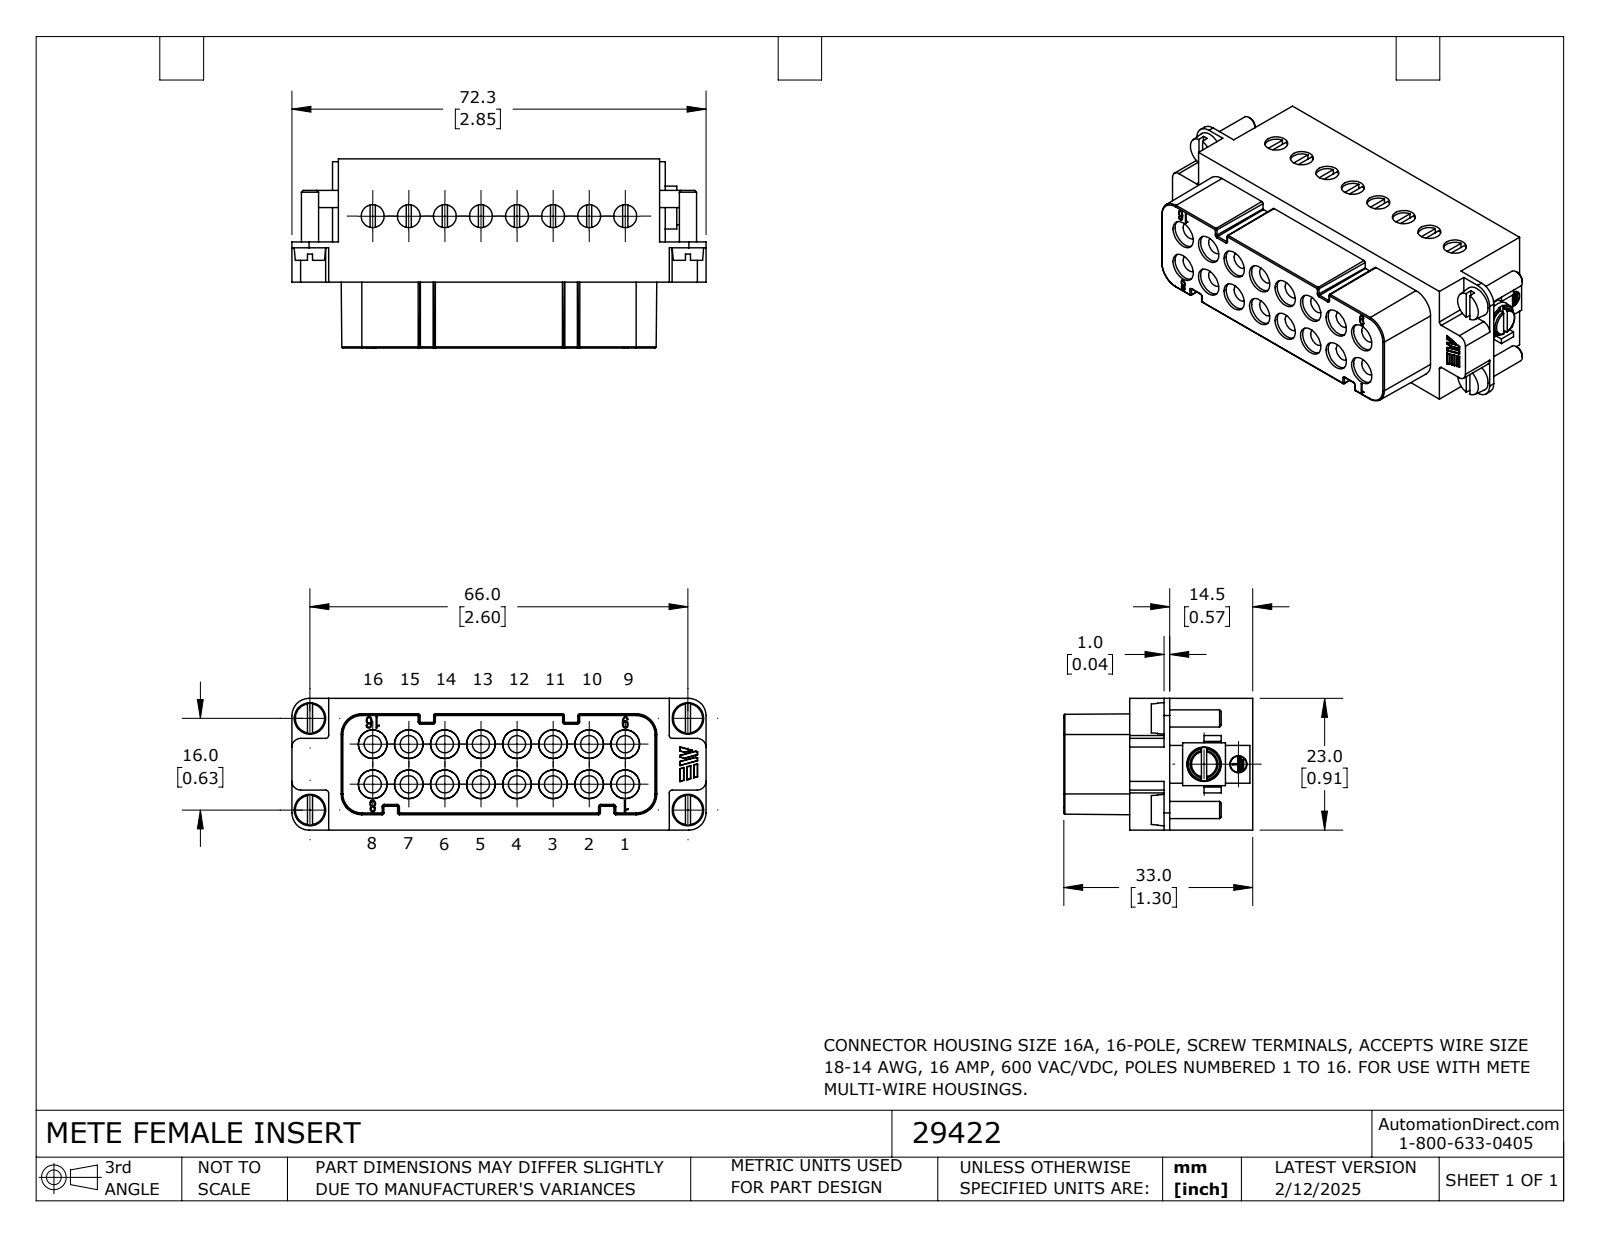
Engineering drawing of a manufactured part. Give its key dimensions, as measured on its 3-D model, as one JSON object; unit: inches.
{"part_name": "29422", "step_written_by": "SolidWorks 2024 (CONFIG_CONTROL_DESIGN)", "units": "inches", "bodies": {"solids": 1, "faces": 570, "planar": 271, "cylindrical": 138, "other": 161}, "overall_size": [2.846, 1.299, 0.906], "volume_in3": 2.244, "surface_area_in2": 22.3, "round_holes": [[0.118, 17], [0.157, 8]], "round_bosses_or_shafts": [[0.118, 4], [0.189, 1], [0.11, 1]], "partial_cylinders_radius": [[0.008, 14], [0.02, 4], [0.059, 4], [0.118, 4]], "face_to_face_distances": [0.906, 1.299, 0.453, 0.846, 0.276, 0.571, 0.728, 0.039, 0.02, 2.209], "hole_center_spacings": [0.248, 0.496, 0.744, 0.371, 0.567, 0.992, 0.793, 1.24]}
